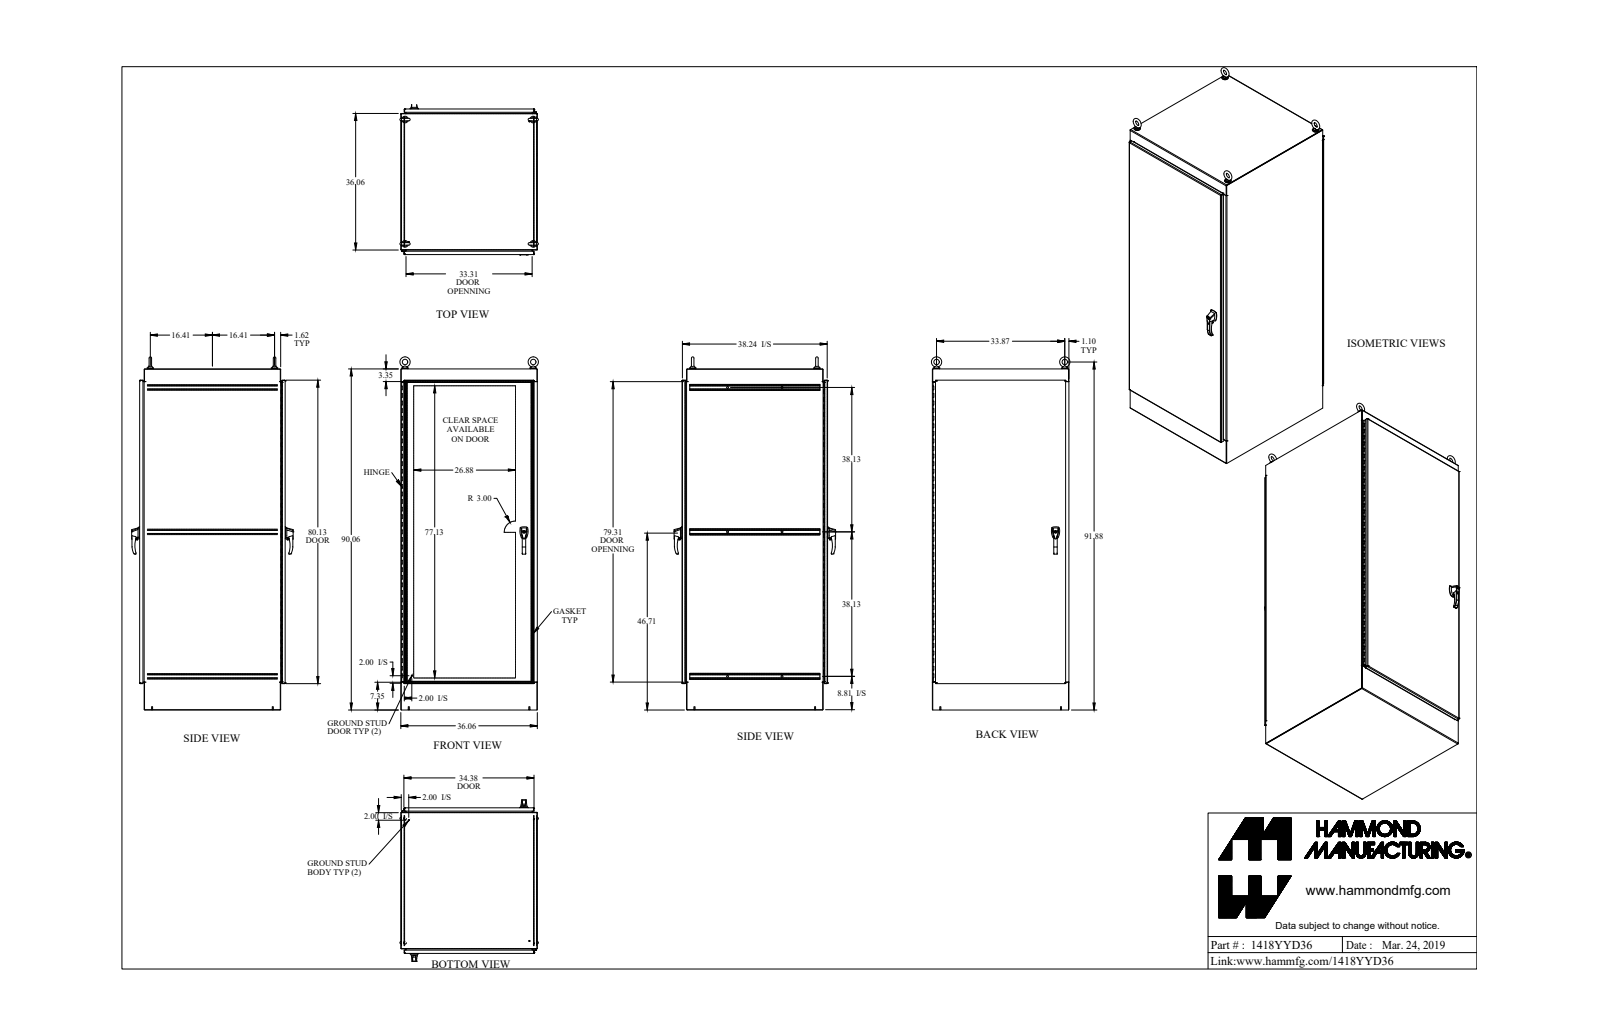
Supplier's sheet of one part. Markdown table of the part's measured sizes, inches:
| quantity | value |
| --- | --- |
| part name | 1418YYD36_Default |
| STEP written by | SolidWorks 2019 (CONFIG_CONTROL_DESIGN) |
| units | inches |
| bodies | 93 solids, 4979 faces (2076 planar, 2577 cylindrical, 326 other) |
| overall size | 93.713 × 42.664 × 37.118 |
| volume | 1 820 in³ |
| surface area | 38 423 in² |
| round holes (diameter × count) | 0.304 × 28, 0.5 × 6, 0.25 × 4, 0.257 × 4, 0.28 × 4, 0.281 × 4, 0.313 × 4, 0.39 × 4, 0.413 × 4, 0.527 × 4, 0.625 × 4, 0.687 × 4 |
| round bosses / shafts (diameter × count) | 0.281 × 8, 1.75 × 4, 1.5 × 4, 1.25 × 4, 1 × 4, 0.75 × 4, 0.738 × 4, 0.63 × 4 |
| partial cylindrical surfaces (radius × count) | 0.125 × 44, 0.043 × 42, 0.138 × 36, 0.018 × 32, 0.048 × 24, 0.143 × 24, 0.06 × 16, 0.318 × 13 |
| main face-to-face distances | 0.095, 35.965, 38.339, 35.87, 36.06, 38.244, 38.434, 89.965, 1.187, 37.152 |
| hole center spacings | 6, 12, 18, 24, 30, 34.853, 36, 36.369 |
